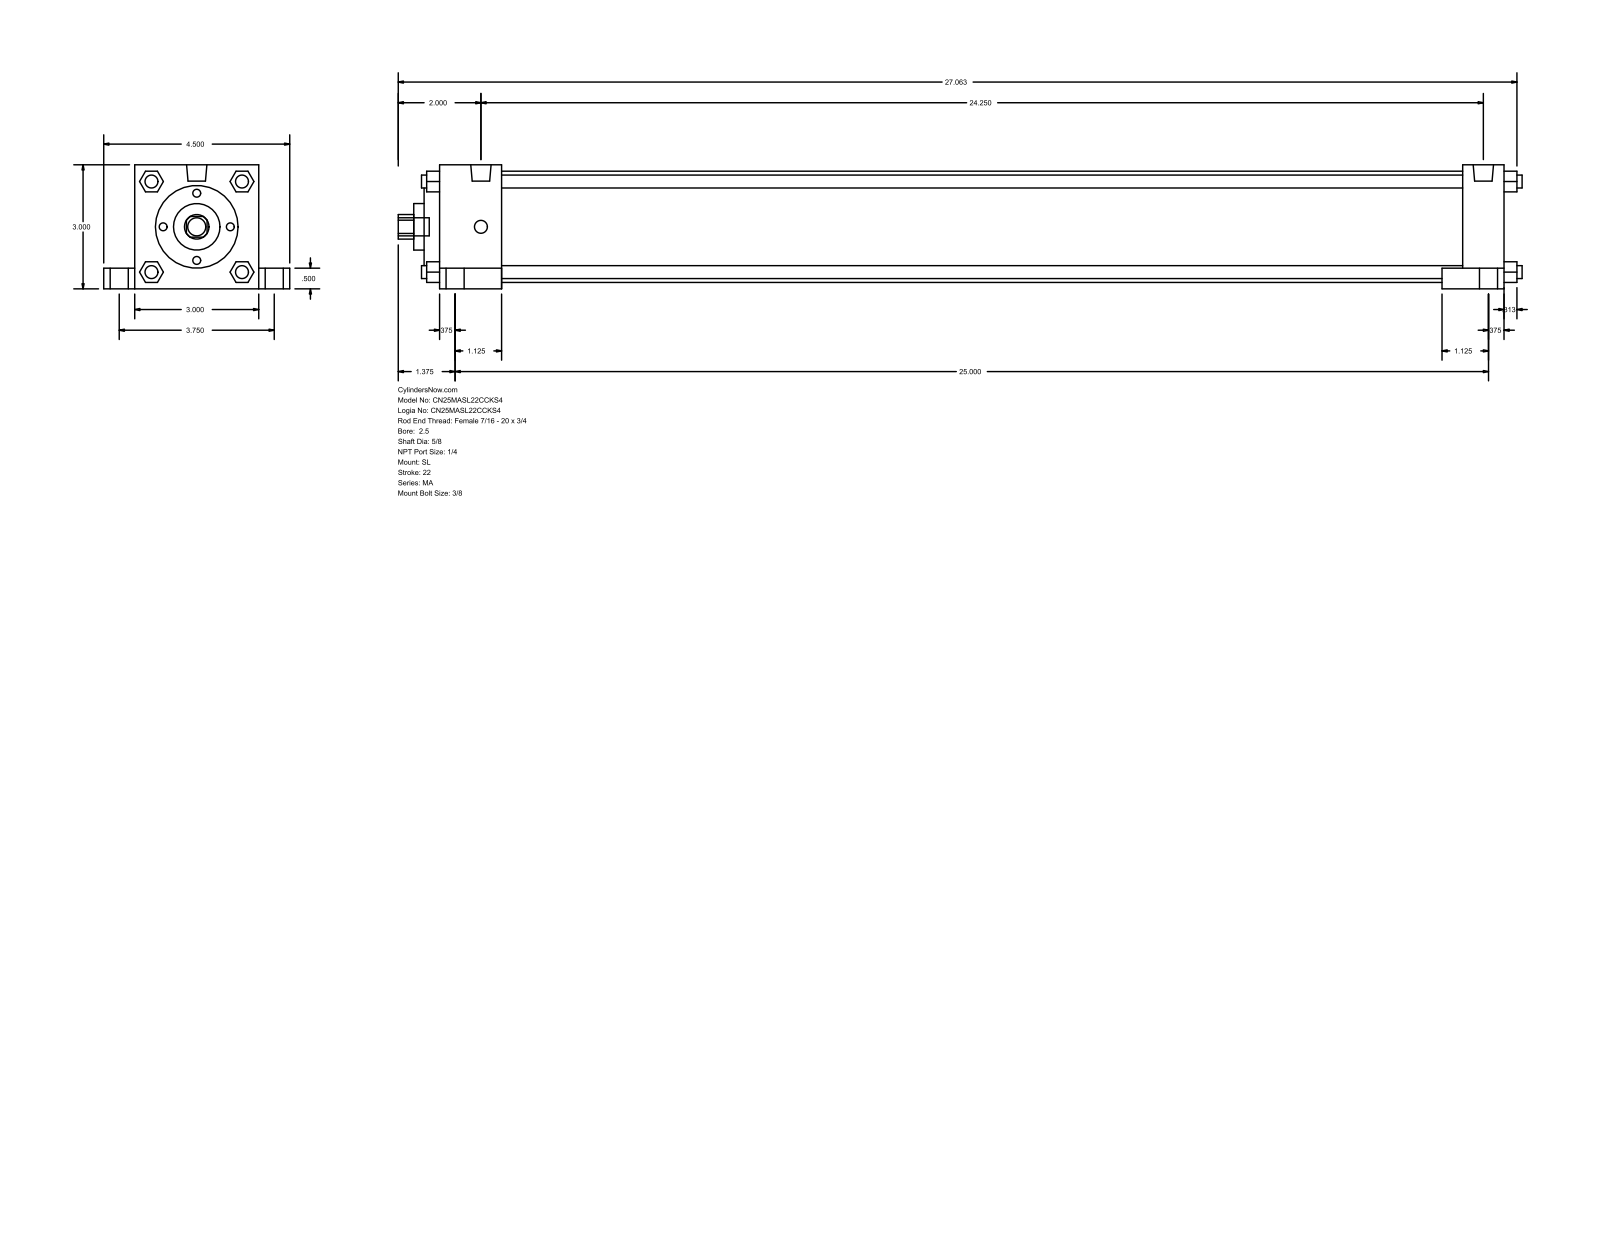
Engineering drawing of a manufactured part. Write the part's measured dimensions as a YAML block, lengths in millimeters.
part_name: "MA_SL__0250_0.625"
step_written_by: "GSSL Pune (CONFIG_CONTROL_DESIGN)"
units: millimeters
bodies: {solids: 0, faces: 150, planar: 113, cylindrical: 37, other: 0}
overall_size: [690.56, 114.3, 76.2]
round_holes:
  - {diameter: 15.88, count: 1}
  - {diameter: 28.57, count: 1}
  - {diameter: 50.8, count: 1}
  - {diameter: 68.33, count: 1}
round_bosses_or_shafts:
  - {diameter: 7.94, count: 8}
  - {diameter: 11.11, count: 5}
  - {diameter: 17.46, count: 4}
  - {diameter: 12.49, count: 2}
partial_cylinders:
  - {radius: 7.54, count: 1}
face_to_face_distances: [76.2, 654.05, 12.7, 590.55, 25.4, 38.1, 615.95, 628.65, 19.05, 63.5]
